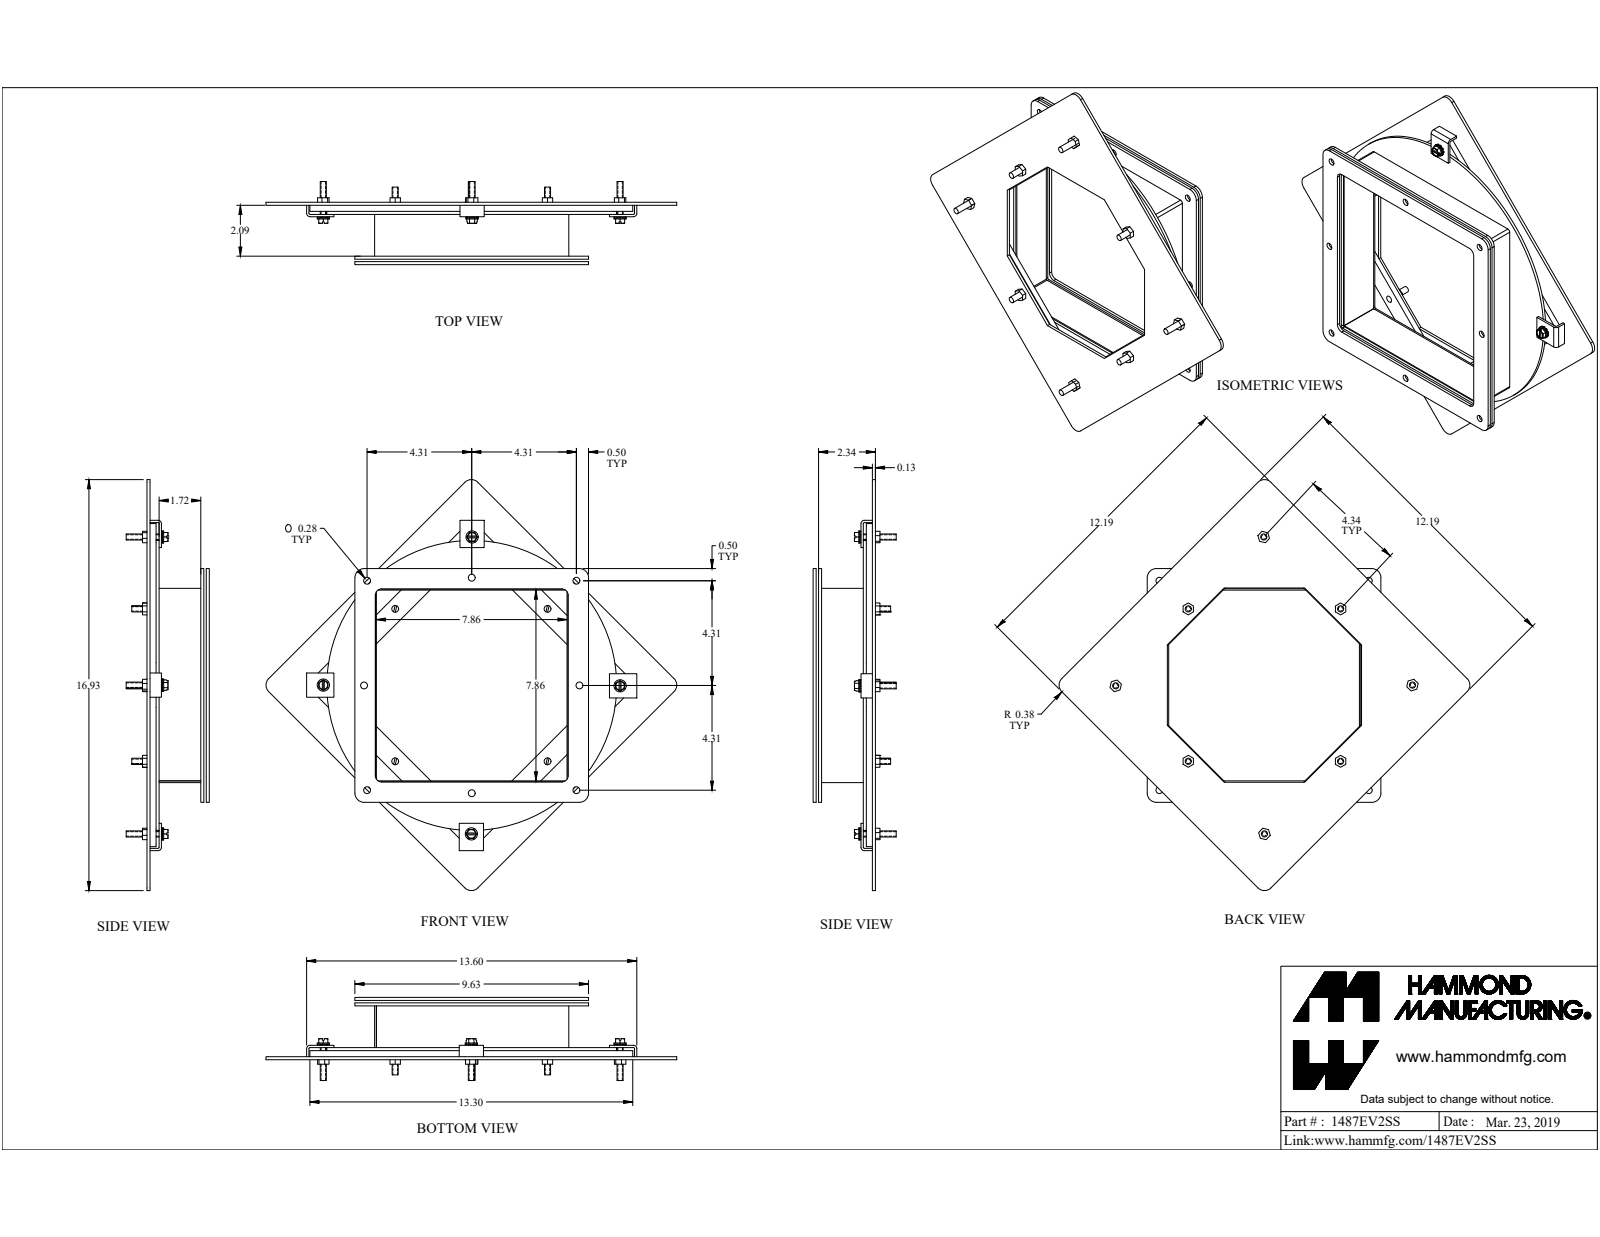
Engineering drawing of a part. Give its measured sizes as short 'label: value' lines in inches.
name: 1487EV2SS
written by: SolidWorks 2019 (CONFIG_CONTROL_DESIGN)
unit: in
bodies: 33 solids, 692 faces (435 planar, 209 cylindrical, 48 other)
size: 16.925 × 16.925 × 3.698
volume: 37.7 in³; area: 664.3 in²
holes: 18× ⌀0.281, 9× ⌀0.196, 5× ⌀0.258, 5× ⌀0.35, 4× ⌀0.312, 4× ⌀0.375
bosses: 9× ⌀0.25, 5× ⌀0.5, 3× ⌀0.455, 1× ⌀11.937, 1× ⌀0.455
rounds: 30× R0.02, 12× R0.375, 8× R0.25, 4× R0.048, 4× R0.062, 4× R0.063, 4× R0.143, 3× R0.036
face distances: 0.125, 0.125, 0.25, 0.375, 1.843, 2.443, 0.375, 0.5, 0.072, 7.928
hole spacings: 9.755, 8.625, 4.314, 4.315, 6.276, 9.755, 4.66, 4.687
